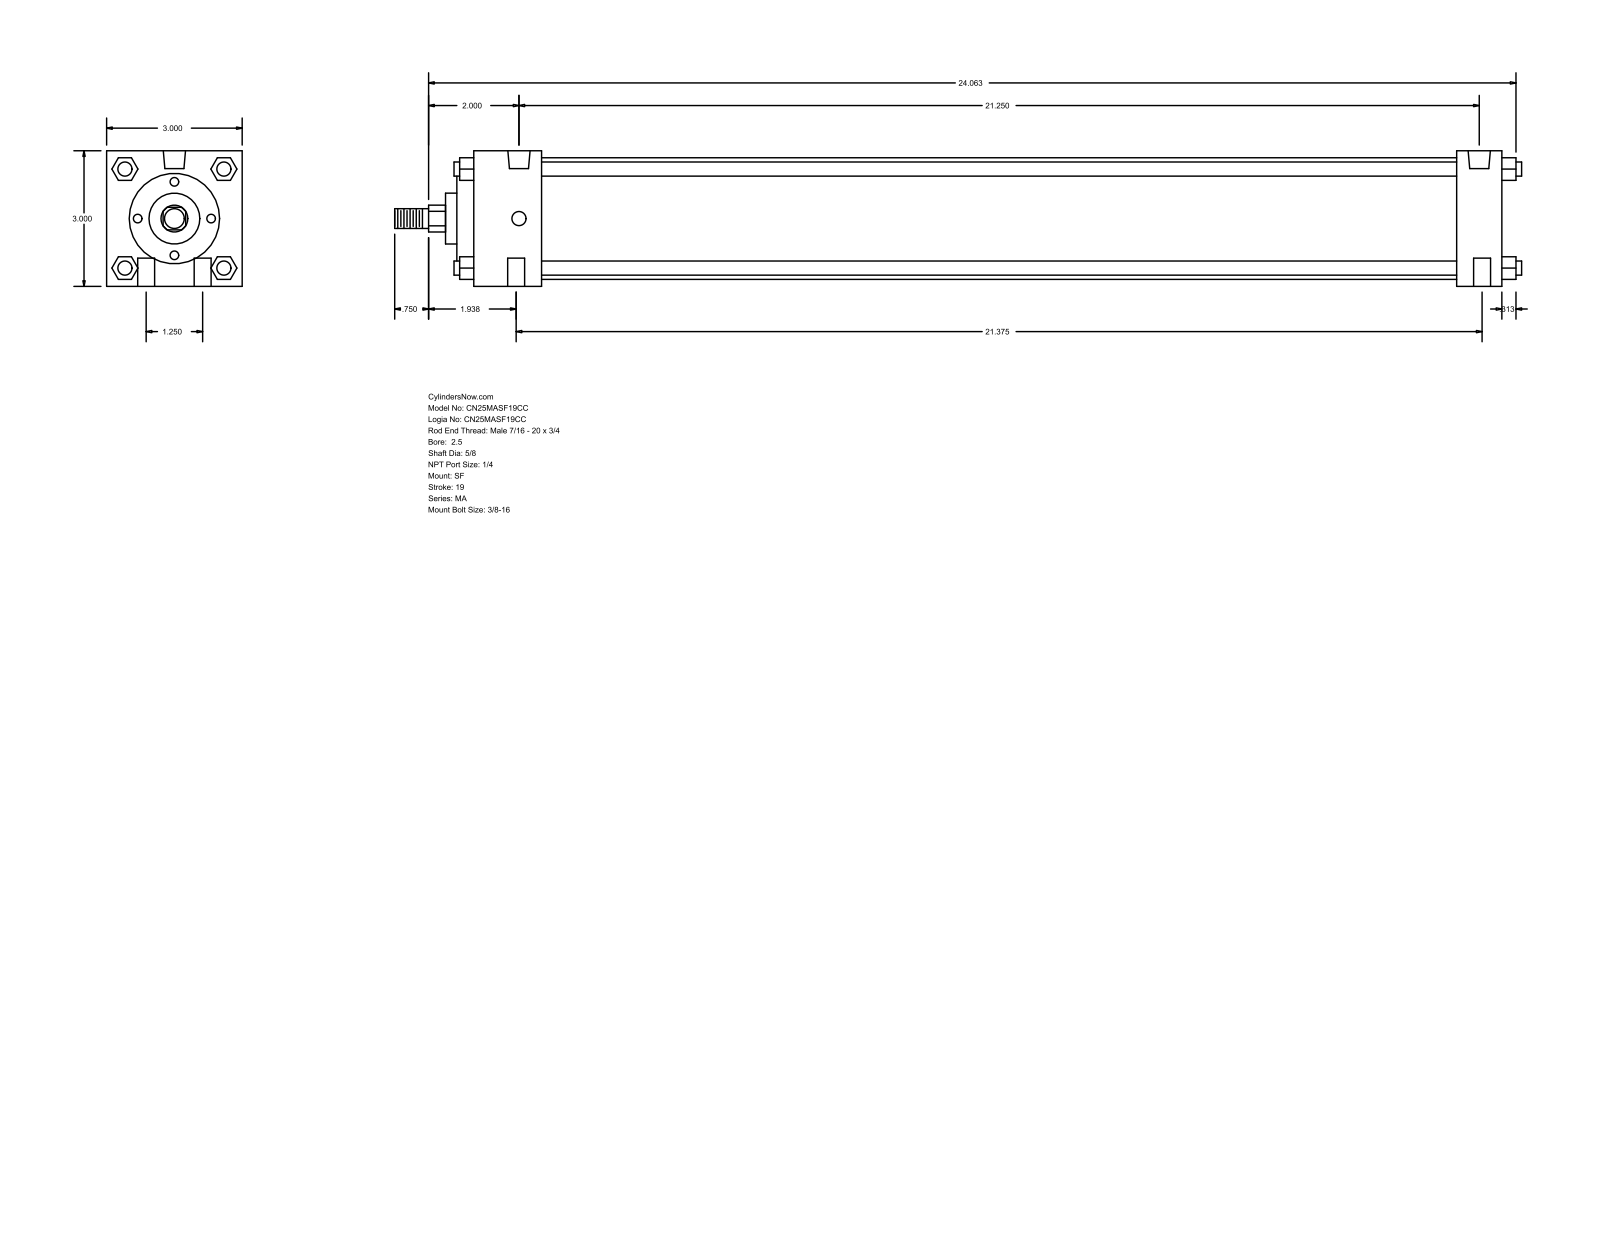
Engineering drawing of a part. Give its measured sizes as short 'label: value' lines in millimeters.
name: MA_SF__0250_0.625
written by: GSSL Pune (CONFIG_CONTROL_DESIGN)
unit: mm
bodies: 0 solids, 126 faces (95 planar, 31 cylindrical, 0 other)
size: 633.41 × 76.2 × 76.2
holes: 4× ⌀9.53, 2× ⌀7.94, 2× ⌀12.49
bosses: 4× ⌀7.94, 1× ⌀68.33, 1× ⌀50.8, 1× ⌀28.57, 1× ⌀15.88, 1× ⌀11.11
rounds: 1× R7.54
face distances: 76.2, 577.85, 25.4, 552.45, 38.1, 514.35, 539.75, 12.7, 9.52, 47.62
hole spacings: 15.96, 541.57, 31.76, 539.75, 542.93, 543.86
